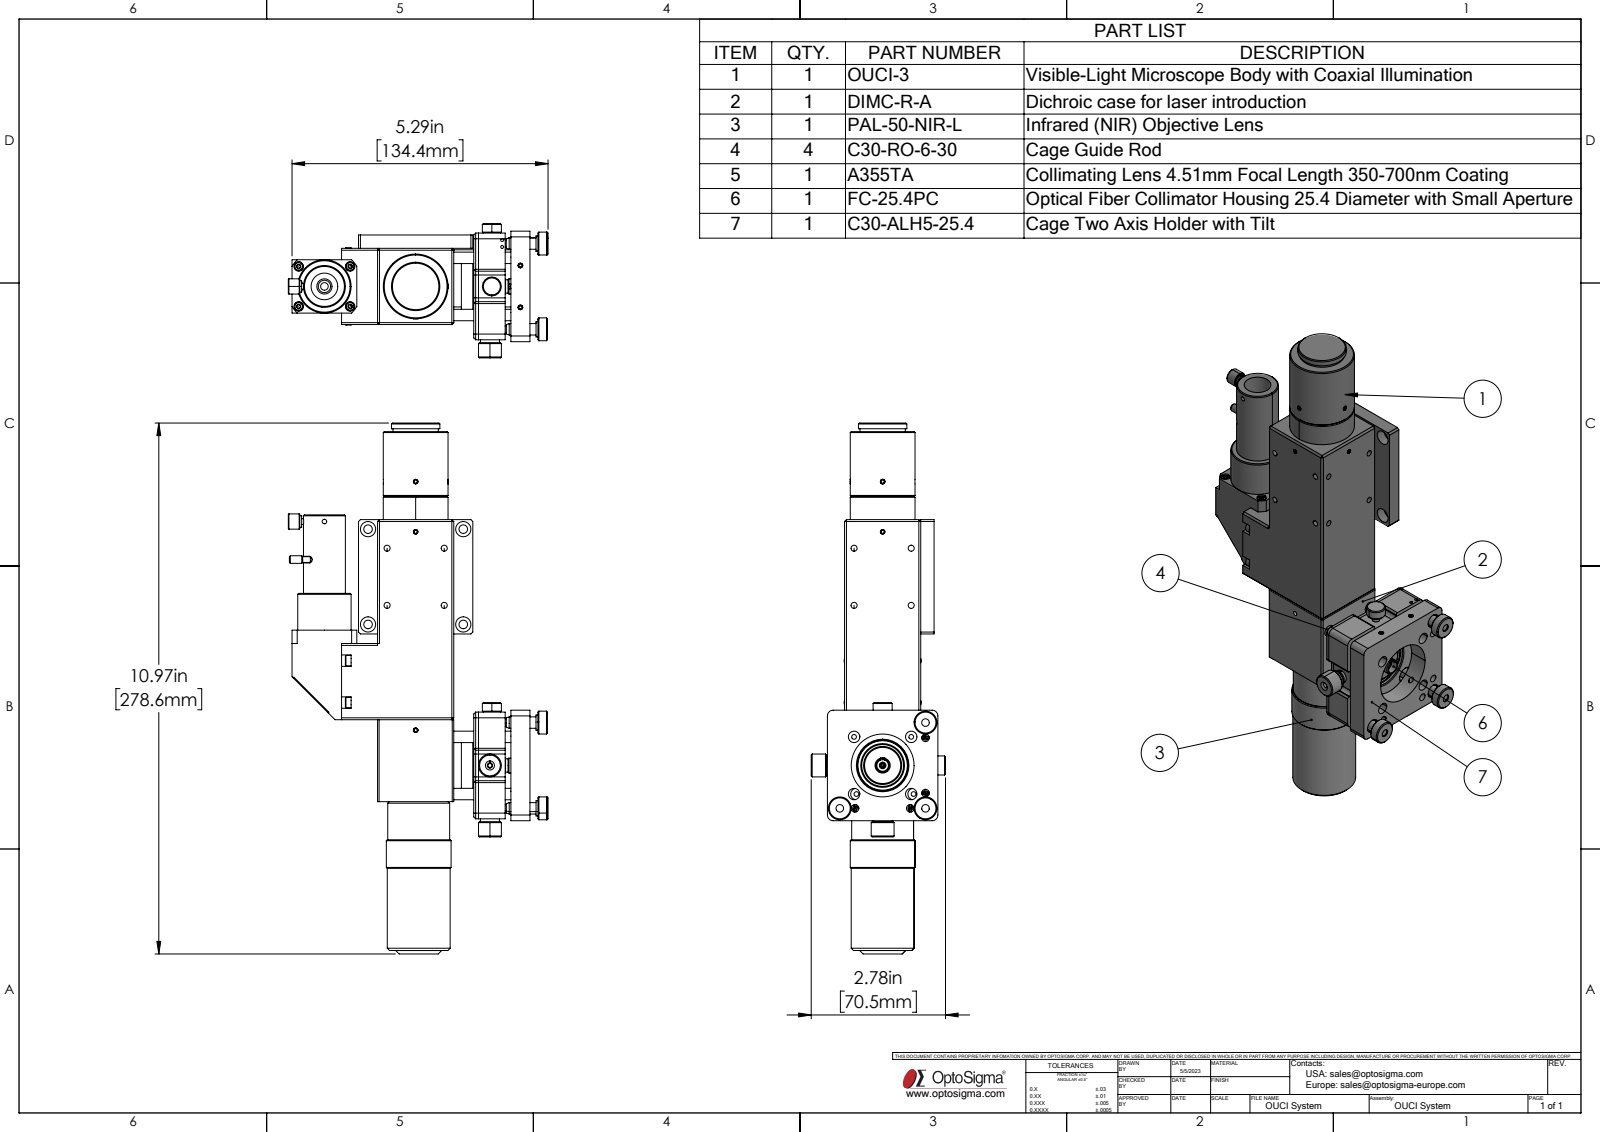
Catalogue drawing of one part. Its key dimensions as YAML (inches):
part_name: "C30-RO-6-30; DIMC-R-A; OUCI-3; C30-ALH5-25.4 (+3 more)"
step_written_by: "SolidWorks 2022 (AUTOMOTIVE_DESIGN)"
units: inches
bodies: {solids: 23, faces: 1566, planar: 834, cylindrical: 470, other: 262}
overall_size: [10.969, 5.368, 2.776]
volume: 30.62
surface_area: 183.2
round_holes:
  - {diameter: 0.315, count: 13}
  - {diameter: 0.043, count: 10}
  - {diameter: 0.126, count: 8}
  - {diameter: 0.157, count: 8}
  - {diameter: 0.177, count: 8}
  - {diameter: 0.197, count: 8}
  - {diameter: 0.236, count: 8}
  - {diameter: 0.098, count: 7}
  - {diameter: 0.039, count: 6}
  - {diameter: 0.094, count: 5}
  - {diameter: 0.097, count: 4}
  - {diameter: 0.295, count: 3}
round_bosses_or_shafts:
  - {diameter: 0.157, count: 10}
  - {diameter: 0.217, count: 8}
  - {diameter: 0.177, count: 8}
  - {diameter: 0.039, count: 8}
  - {diameter: 0.276, count: 6}
  - {diameter: 0.236, count: 6}
  - {diameter: 0.472, count: 5}
  - {diameter: 0.315, count: 5}
partial_cylinders:
  - {radius: 0.079, count: 32}
  - {radius: 0.039, count: 18}
  - {radius: 0.02, count: 16}
  - {radius: 0.118, count: 12}
  - {radius: 0.087, count: 8}
  - {radius: 0.138, count: 8}
  - {radius: 0.157, count: 4}
  - {radius: 0.236, count: 4}
face_to_face_distances: [1.575, 0.394, 1.693, 0.512, 1.85, 0.118, 0.276, 0.197, 1.181, 0.157]
hole_center_spacings: [1.181, 1.476, 0.157, 0.835, 1.142, 1.623, 1.67, 0.315]
